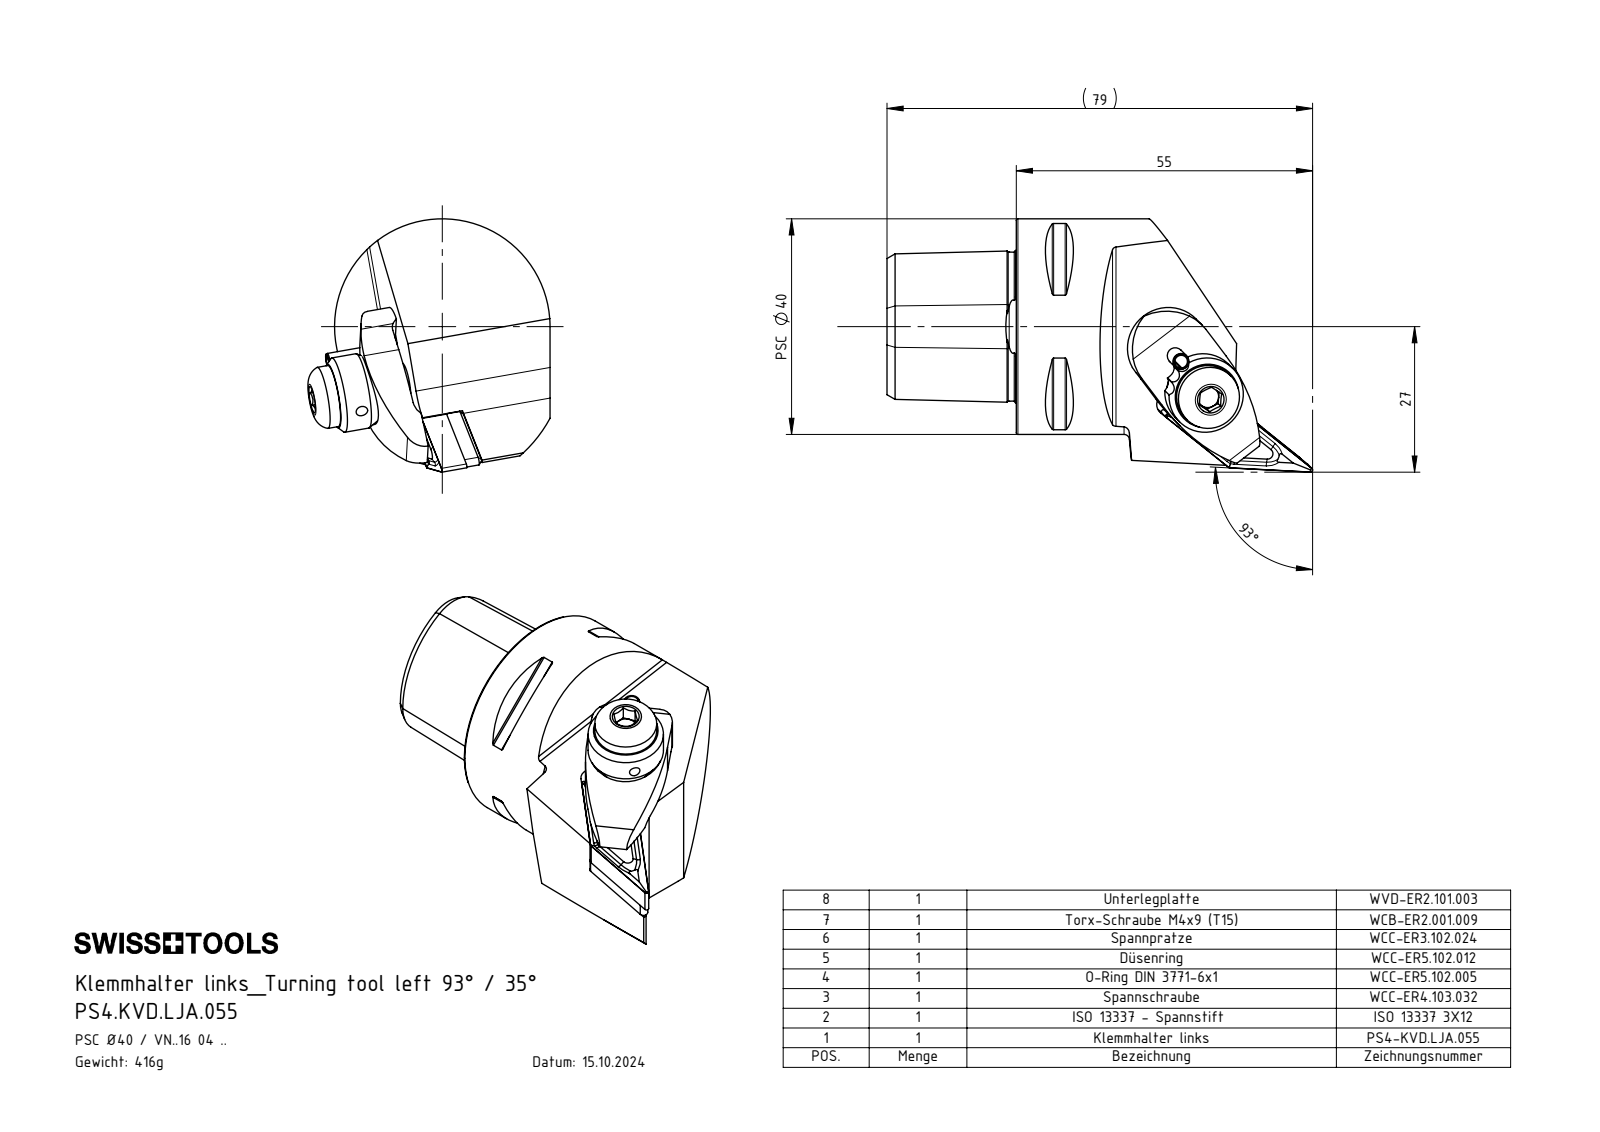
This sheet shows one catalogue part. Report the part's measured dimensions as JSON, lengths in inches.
{"part_name": "WCC-ER3.102.024_C; WCB-ER2.001.009_A; WCC-ER5.102.012_B; ISO 13337 - 3 x 12_PreviewCfg (+7 more)", "step_written_by": "SolidWorks 2022 (AUTOMOTIVE_DESIGN)", "units": "inches", "bodies": {"solids": 10, "faces": 426, "planar": 109, "cylindrical": 132, "other": 185}, "overall_size": [3.11, 1.85, 1.77], "volume_in3": 3.173, "surface_area_in2": 27.87, "round_holes": [[0.079, 3], [0.276, 2], [0.094, 1], [0.118, 1], [0.13, 1], [0.15, 1], [0.157, 1], [0.165, 1], [0.181, 1], [0.195, 1], [0.197, 1], [0.236, 1]], "round_bosses_or_shafts": [[0.157, 2], [0.118, 2], [1.575, 1], [0.551, 1], [0.453, 1], [0.268, 1], [0.236, 1], [0.207, 1]], "partial_cylinders_radius": [[0.012, 8], [0.013, 6], [0.023, 6], [0.016, 4], [0.031, 3], [0.059, 3], [0.118, 3], [0.079, 2]], "face_to_face_distances": [0.176, 0.227, 0.051, 0.787, 0.945, 1.732, 0.359, 0.125, 0.301, 0.352], "hole_center_spacings": [0.316, 0.878, 0.323, 0.323, 0.555, 0.556, 0.562, 0.563]}
